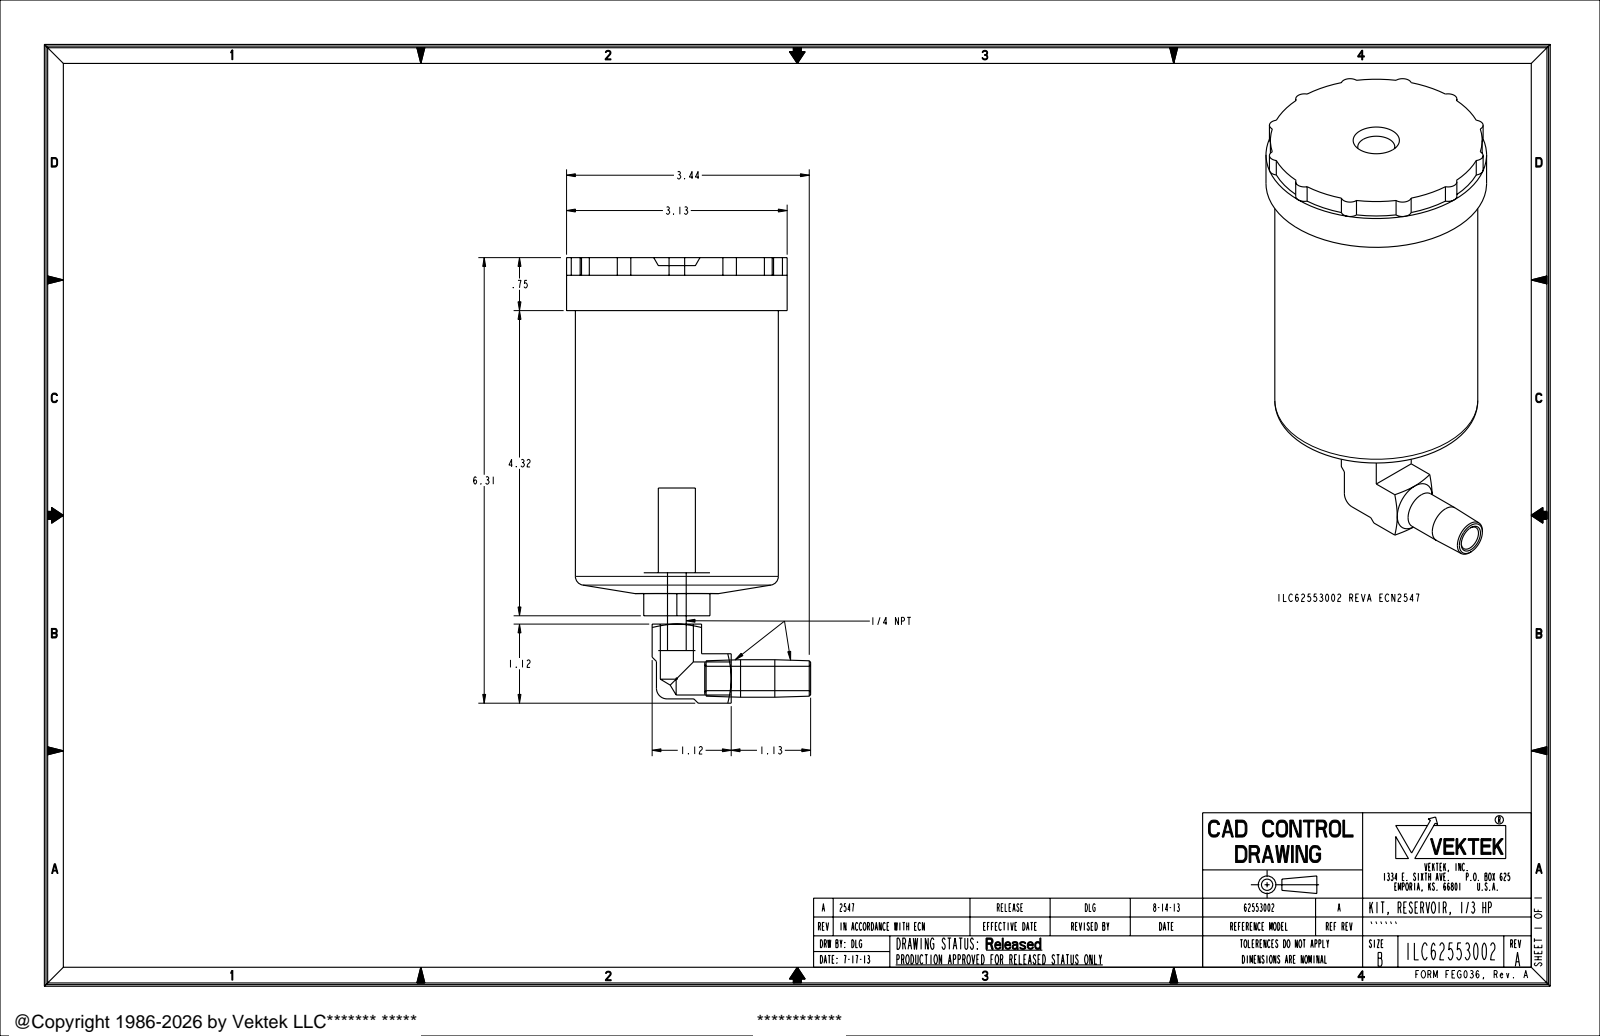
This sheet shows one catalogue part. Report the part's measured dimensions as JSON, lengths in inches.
{"part_name": "ILC62553002", "step_written_by": "PRO/ENGINEER BY PARAMETRIC TECHNOLOGY CORPORATION, 2007460 (AUTOMOTIVE_DESIGN_CC2)", "units": "inches", "bodies": {"solids": 0, "faces": 116, "planar": 39, "cylindrical": 45, "other": 32}, "overall_size": [6.308, 3.458, 3.125], "round_holes": [[0.468, 2], [0.265, 1], [0.345, 1], [0.525, 1]], "round_bosses_or_shafts": [[3.125, 1], [2.875, 1], [0.531, 1]], "partial_cylinders_radius": [[0.125, 12], [0.15, 1], [1.5, 1]], "face_to_face_distances": [0.7, 0.75, 3.711, 4.461, 0.609, 4.32, 5.07, 0.061, 0.639, 0.938]}
